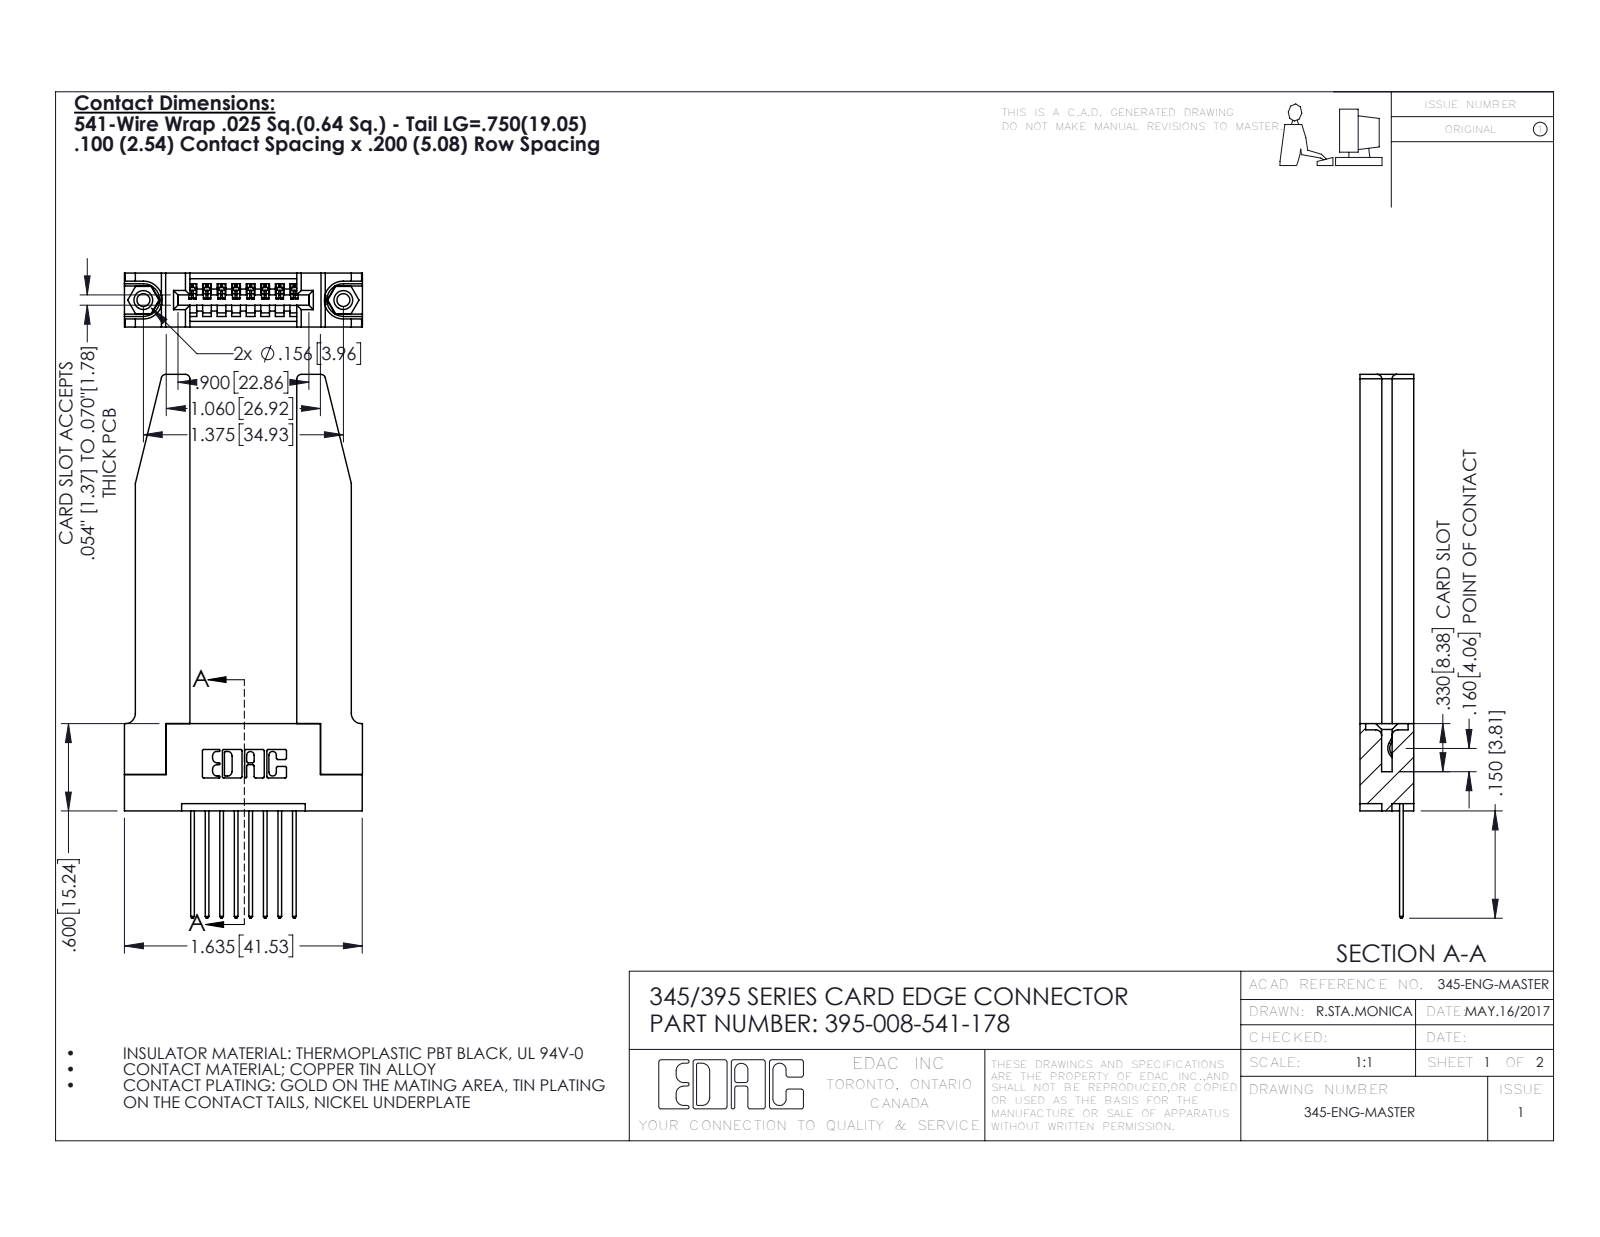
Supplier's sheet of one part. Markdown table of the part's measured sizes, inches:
| quantity | value |
| --- | --- |
| part name | 345-292-001_345-293-141; 345-250-001_345-250-001-102; 345 Part_Flush Mounting Lugs - 0.156 Dia-TH; 345-220-078_345-220-078 (+1 more) |
| STEP written by | SolidWorks 2016 (CONFIG_CONTROL_DESIGN) |
| units | inches |
| bodies | 13 solids, 824 faces (542 planar, 230 cylindrical, 52 other) |
| overall size | 3.737 × 1.636 × 0.37 |
| volume | 0.7 in³ |
| surface area | 17.75 in² |
| round holes (diameter × count) | 0.089 × 2, 0.125 × 2, 0.156 × 2, 0.064 × 1 |
| round bosses / shafts (diameter × count) | 0.155 × 2 |
| partial cylindrical surfaces (radius × count) | 0.01 × 22, 0.006 × 16, 0.01 × 16, 0.03 × 8, 0.007 × 6, 0.031 × 6, 0.026 × 3, 0.031 × 2 |
| main face-to-face distances | 0.37, 0.072, 0.298, 0.15, 0.22, 0.148, 0.735, 0.077, 0.2, 0.098 |
| hole center spacings | 0.27, 1.144, 1.375 |
